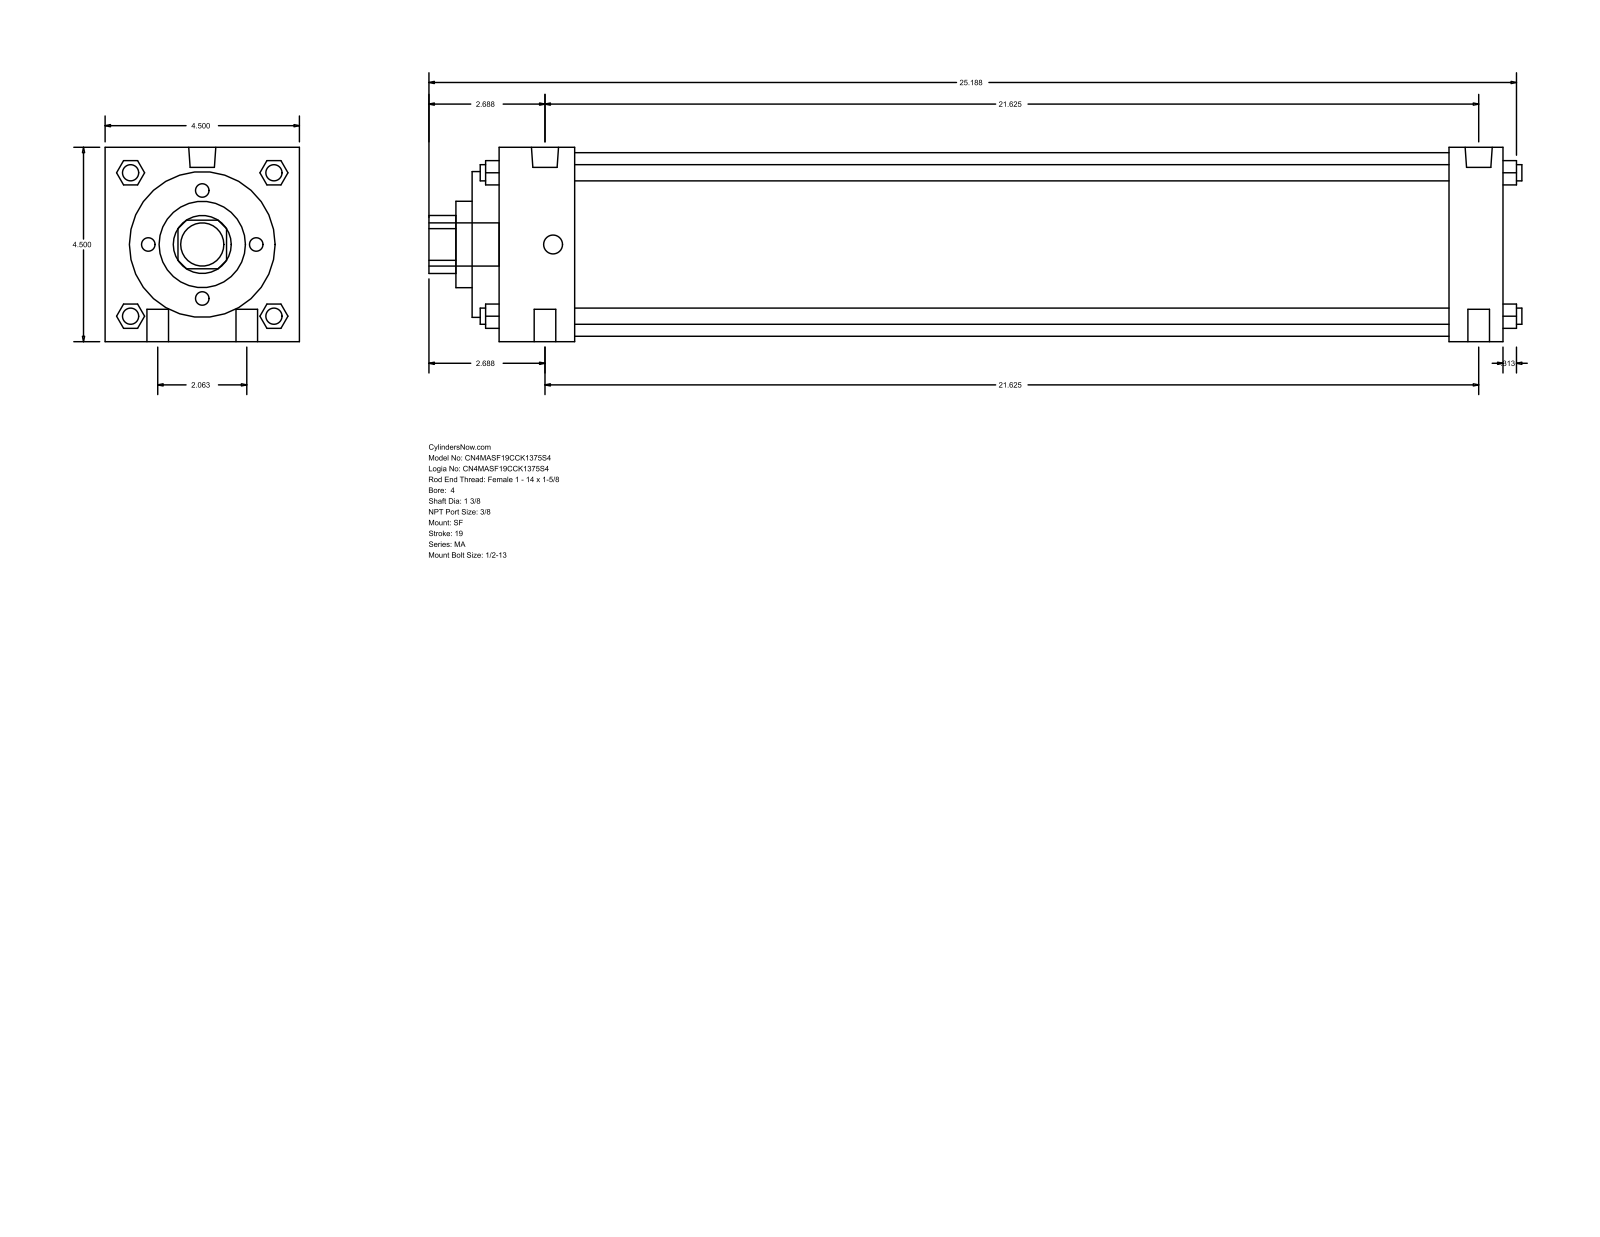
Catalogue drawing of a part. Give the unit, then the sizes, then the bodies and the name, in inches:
Units: inches
Overall size (bounding box): 25.313 × 4.5 × 4.5
Round holes (diameter × count): ⌀1.375 ×1, ⌀2 ×1, ⌀3.375 ×1, ⌀4.25 ×1
Round bosses / shafts (diameter × count): ⌀0.5 ×4, ⌀0.375 ×4, ⌀0.627 ×2, ⌀0.437 ×2, ⌀1 ×1
Partial cylindrical surfaces — rounded edges, fillets, slot ends (radius × count): R0.672 ×1
Main face-to-face distances: 4.5, 23.25, 0.625, 23.875, 22.625, 22, 1.25, 2.375, 1.75, 20.25
Bodies: 0 solids, 126 faces (95 planar, 31 cylindrical, 0 other)
Part name (STEP PRODUCT): MA_SF__0400_1.375
STEP written by: GSSL Pune (CONFIG_CONTROL_DESIGN)
